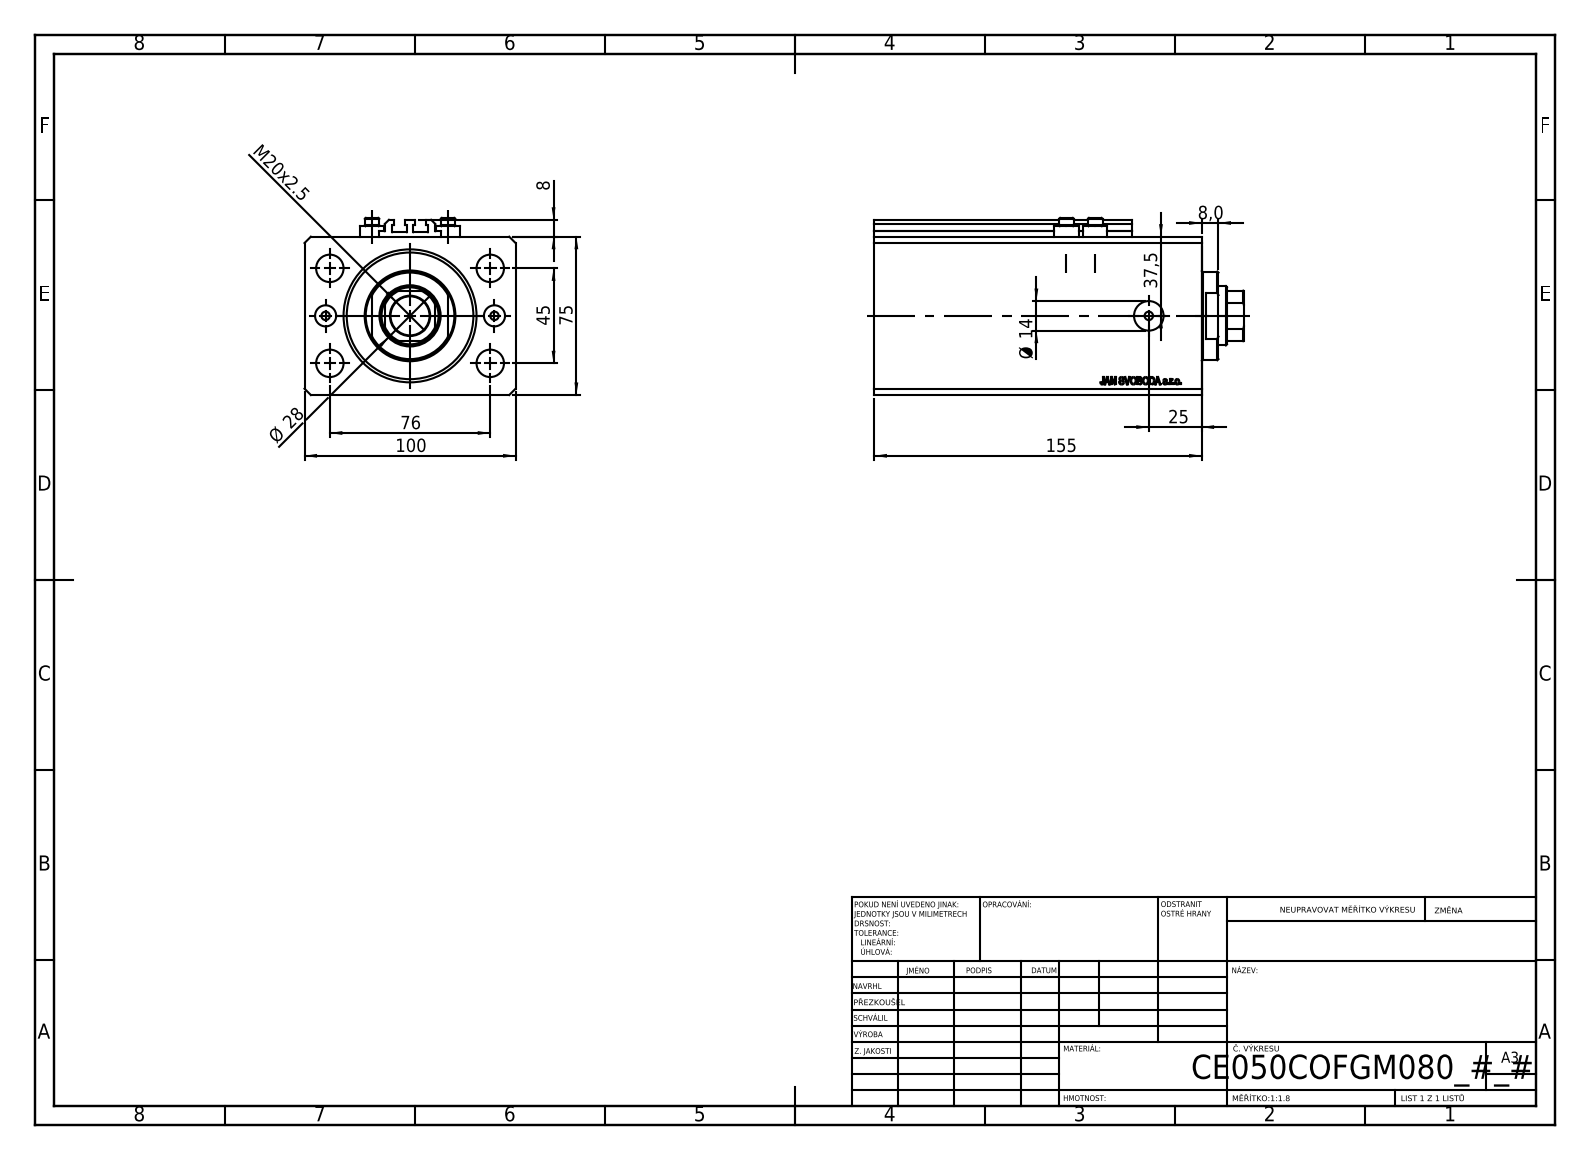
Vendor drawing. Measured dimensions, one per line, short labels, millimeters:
name: V250CE_C_VCP; V250CE_VC_C; V250CE_C_Body; ALLEN BOLT V250CE
written by: SolidWorks 2019 (CONFIG_CONTROL_DESIGN)
unit: mm
bodies: 8 solids, 1034 faces (504 planar, 86 cylindrical, 444 other)
size: 175 × 100 × 84
volume: 991 895 mm³; area: 168 109 mm²
holes: 8× ⌀4, 4× ⌀13, 2× ⌀10, 2× ⌀14, 1× ⌀18.5, 1× ⌀28, 1× ⌀50, 1× ⌀63
bosses: 4× ⌀11.6, 4× ⌀7, 1× ⌀42
rounds: 10× R0.2, 1× R13.5
face distances: 75, 100, 155, 11.9, 143.1, 20, 135, 123.1, 80, 8
hole spacings: 22.59, 44.16, 81.18, 13.6, 36, 38.48, 40, 45
